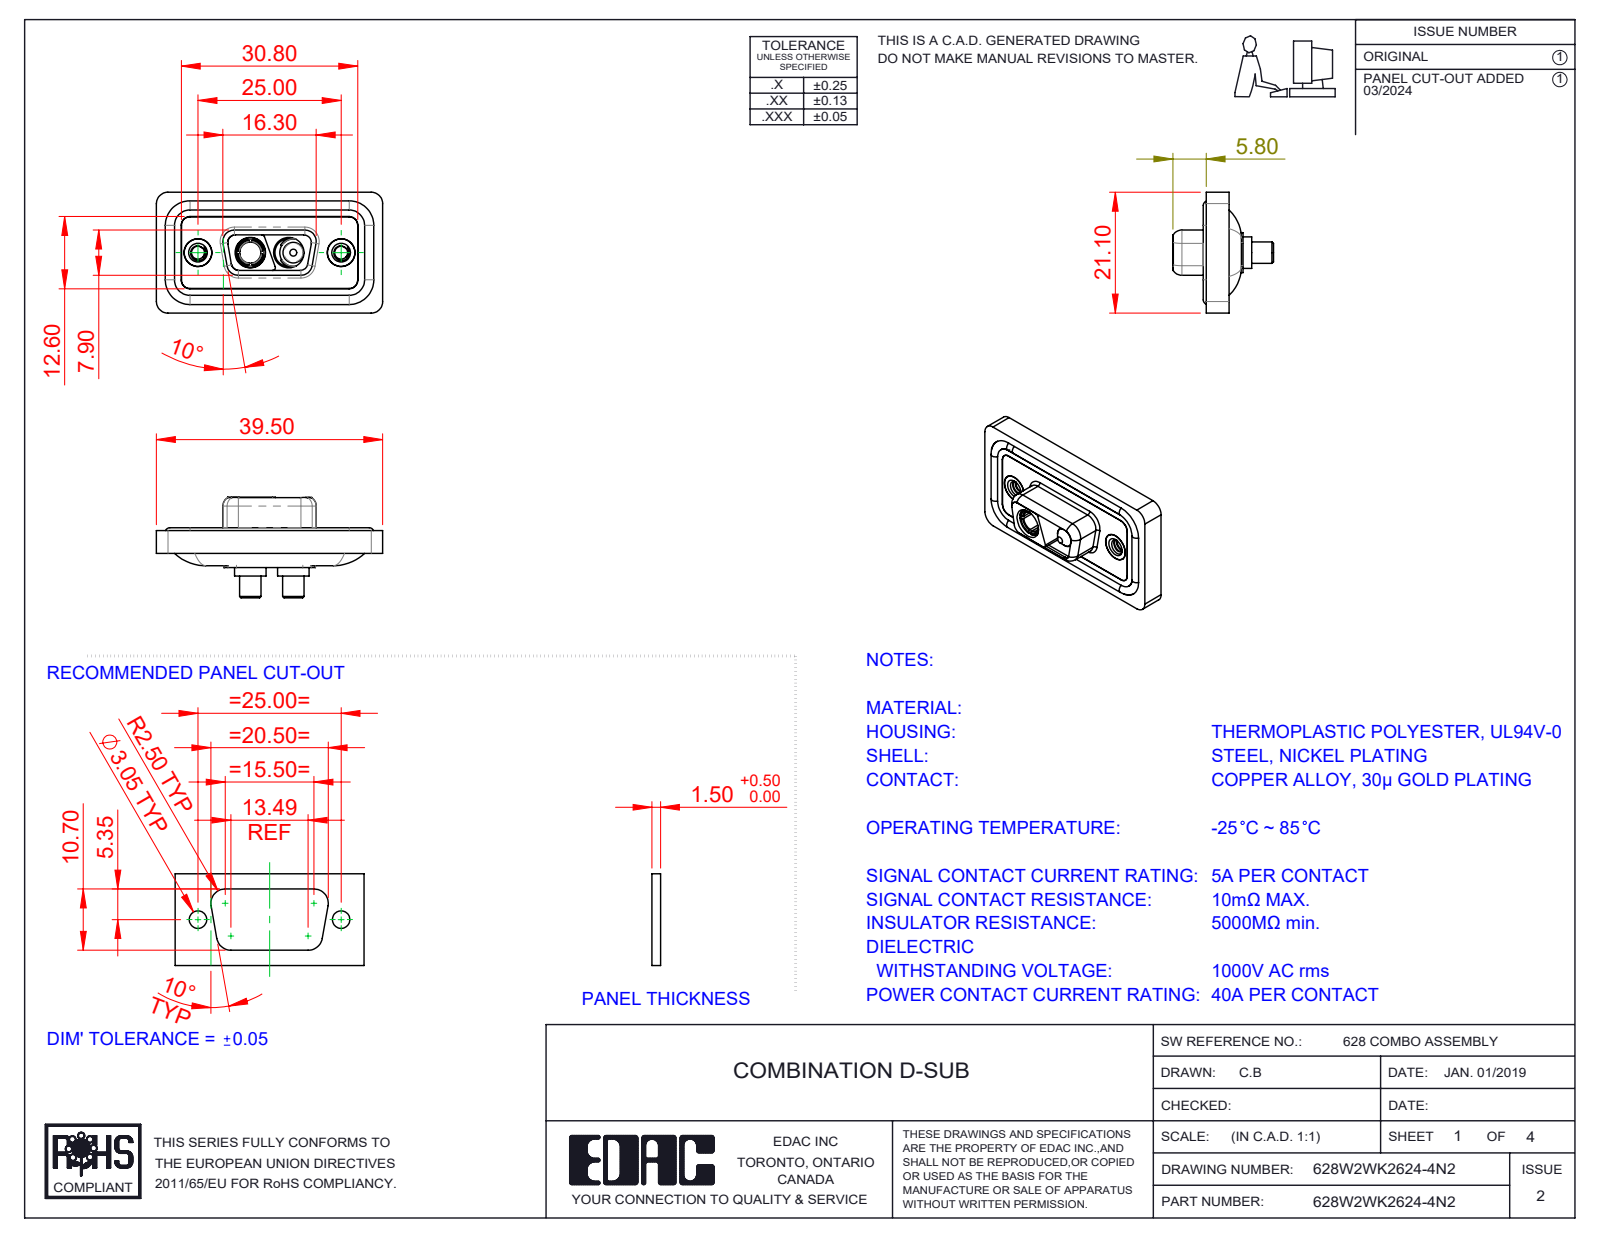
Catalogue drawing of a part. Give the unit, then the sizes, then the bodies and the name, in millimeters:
Units: millimetres
Overall size (bounding box): 39.5 × 21.1 × 17.55
Round holes (diameter × count): ⌀4.85 ×4, ⌀2.26 ×2, ⌀4 ×2, ⌀4.05 ×2, ⌀5 ×2, ⌀5.3 ×2, ⌀3.7 ×1
Round bosses / shafts (diameter × count): ⌀1.6 ×4, ⌀5.5 ×2, ⌀5.2 ×2, ⌀4.95 ×2, ⌀4.8 ×2, ⌀4.75 ×2, ⌀3.75 ×2, ⌀4.96 ×1
Partial cylindrical surfaces — rounded edges, fillets, slot ends (radius × count): R1.5 ×22, R2 ×18, R1.35 ×8, R1.6 ×8, R0.5 ×6, R0.25 ×4, R0.6 ×4, R0.65 ×4
Main face-to-face distances: 0.4, 1.1, 2.9, 1.6, 0.5, 1.8, 5.65, 5.35, 3.1, 1.5
Hole centre spacings: 9.14, 15.86, 6.72, 25
Volume: 4 640 mm³ · Surface area: 7 365 mm²
Bodies: 11 solids, 500 faces (144 planar, 231 cylindrical, 125 other)
Part name (STEP PRODUCT): 628Combo Housing_2WK2; Power Socket_40A S; Power Pin_40A S; 628Combo Shell Rear_09 Contacts (+4 more)
STEP written by: SolidWorks 2023 (CONFIG_CONTROL_DESIGN)
